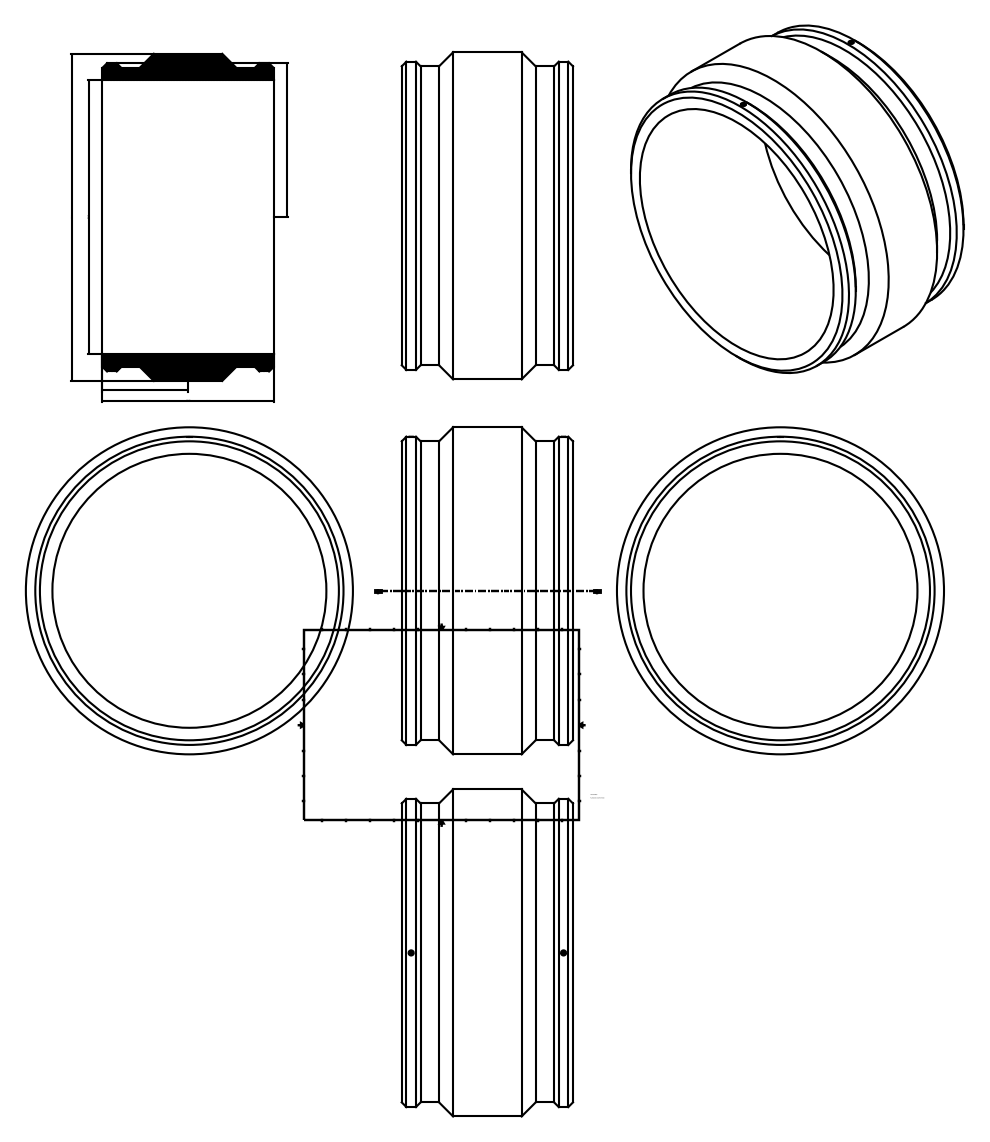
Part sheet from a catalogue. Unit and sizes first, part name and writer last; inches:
Units: inches
Overall size (bounding box): 37.598 × 37.598 × 19.685
Round holes (diameter × count): ⌀0.394 ×2, ⌀31.496 ×1
Round bosses / shafts (diameter × count): ⌀0.591 ×2, ⌀0.157 ×2, ⌀37.598 ×1, ⌀35.433 ×1, ⌀34.37 ×1
Main face-to-face distances: 19.685, 0.551, 0.433, 0.118
Hole centre spacings: 17.52
Volume: 4 843 in³ · Surface area: 4 728 in²
Bodies: 1 solid, 28 faces (8 planar, 14 cylindrical, 6 other)
Part name (STEP PRODUCT): 490103800
STEP written by: Autodesk Inventor 2015 (AUTOMOTIVE_DESIGN)
